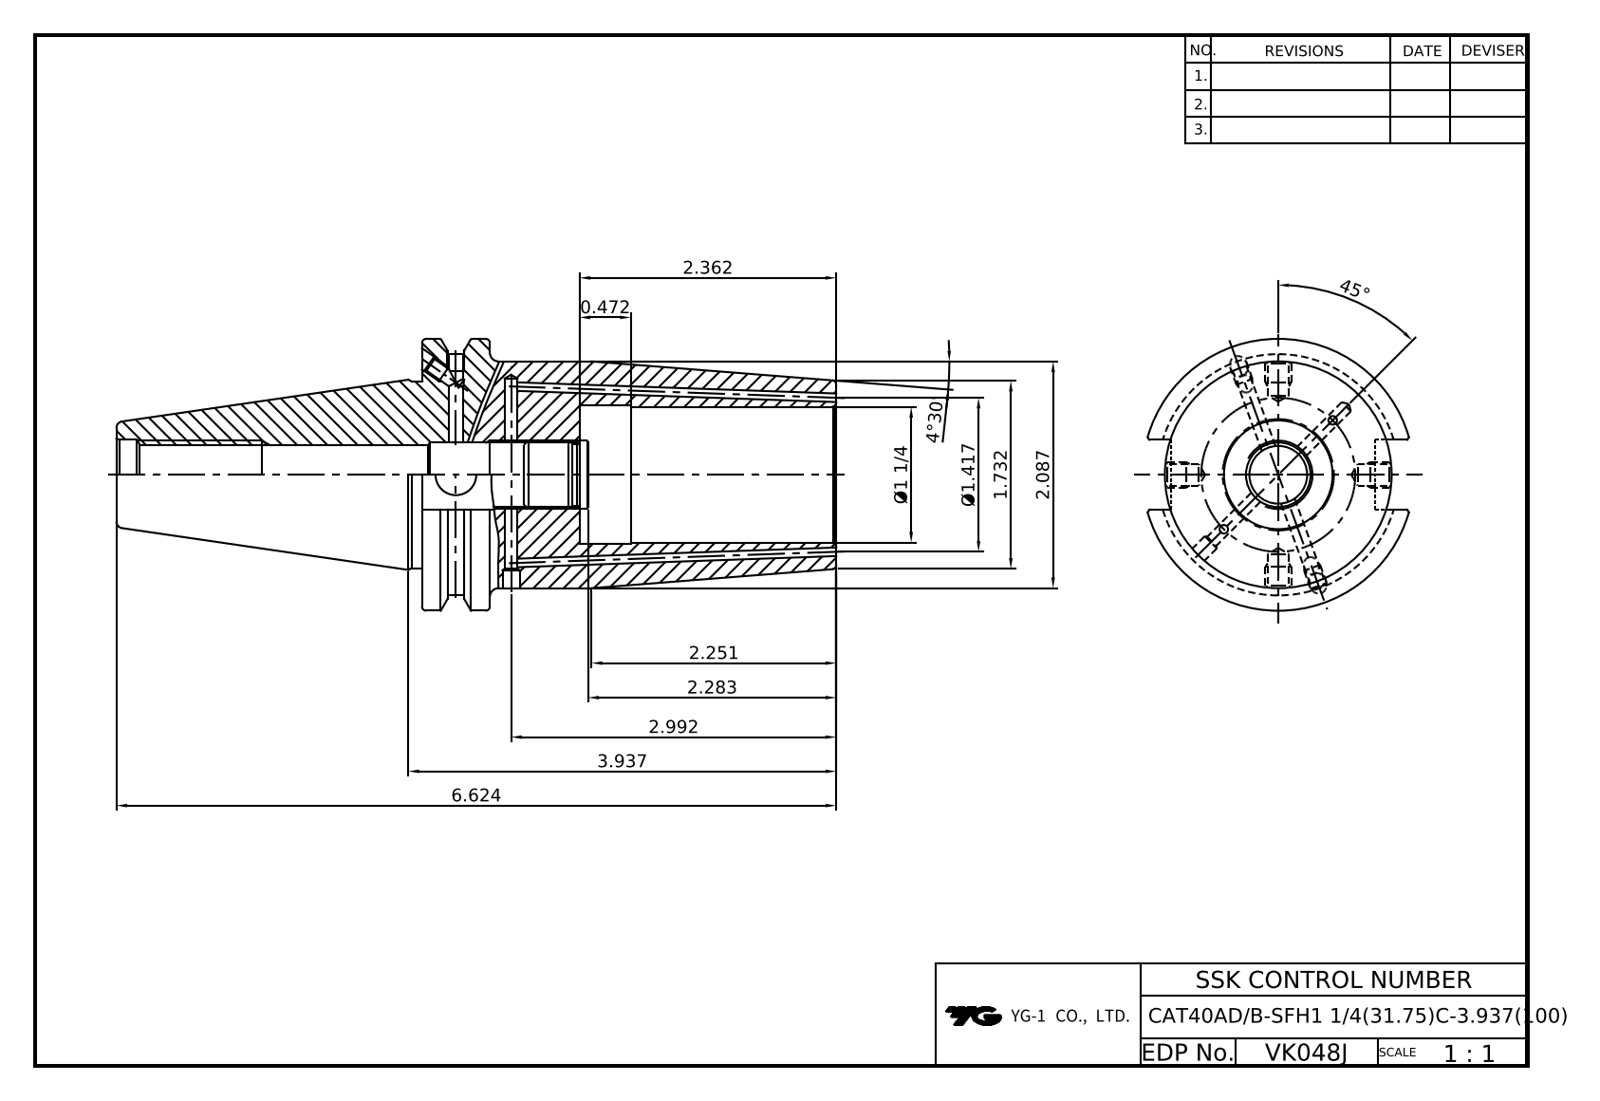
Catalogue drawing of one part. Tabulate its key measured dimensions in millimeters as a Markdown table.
| quantity | value |
| --- | --- |
| part name | LO-CAT40ADB-SFH31.75C-100 |
| STEP written by | Autodesk Inventor 2025 (AUTOMOTIVE_DESIGN) |
| units | millimeters |
| bodies | 1 solid, 90 faces (34 planar, 32 cylindrical, 24 other) |
| overall size | 168.25 × 63.5 × 61.09 |
| volume | 205 378 mm³ |
| surface area | 40 753 mm² |
| round holes (diameter × count) | 3.24 × 4, 2.5 × 2, 4 × 2, 4.2 × 2, 9.53 × 1, 13.39 × 1, 14.92 × 1, 16.3 × 1, 31.75 × 1, 32.95 × 1 |
| round bosses / shafts (diameter × count) | 63.5 × 1, 53 × 1, 43.6 × 1 |
| partial cylindrical surfaces (radius × count) | 8.19 × 1, 28.15 × 1 |
| main face-to-face distances | 36.83, 96.83, 60, 15.88, 20.95, 80.95, 47.6, 16.38, 71.42, 87.3 |
